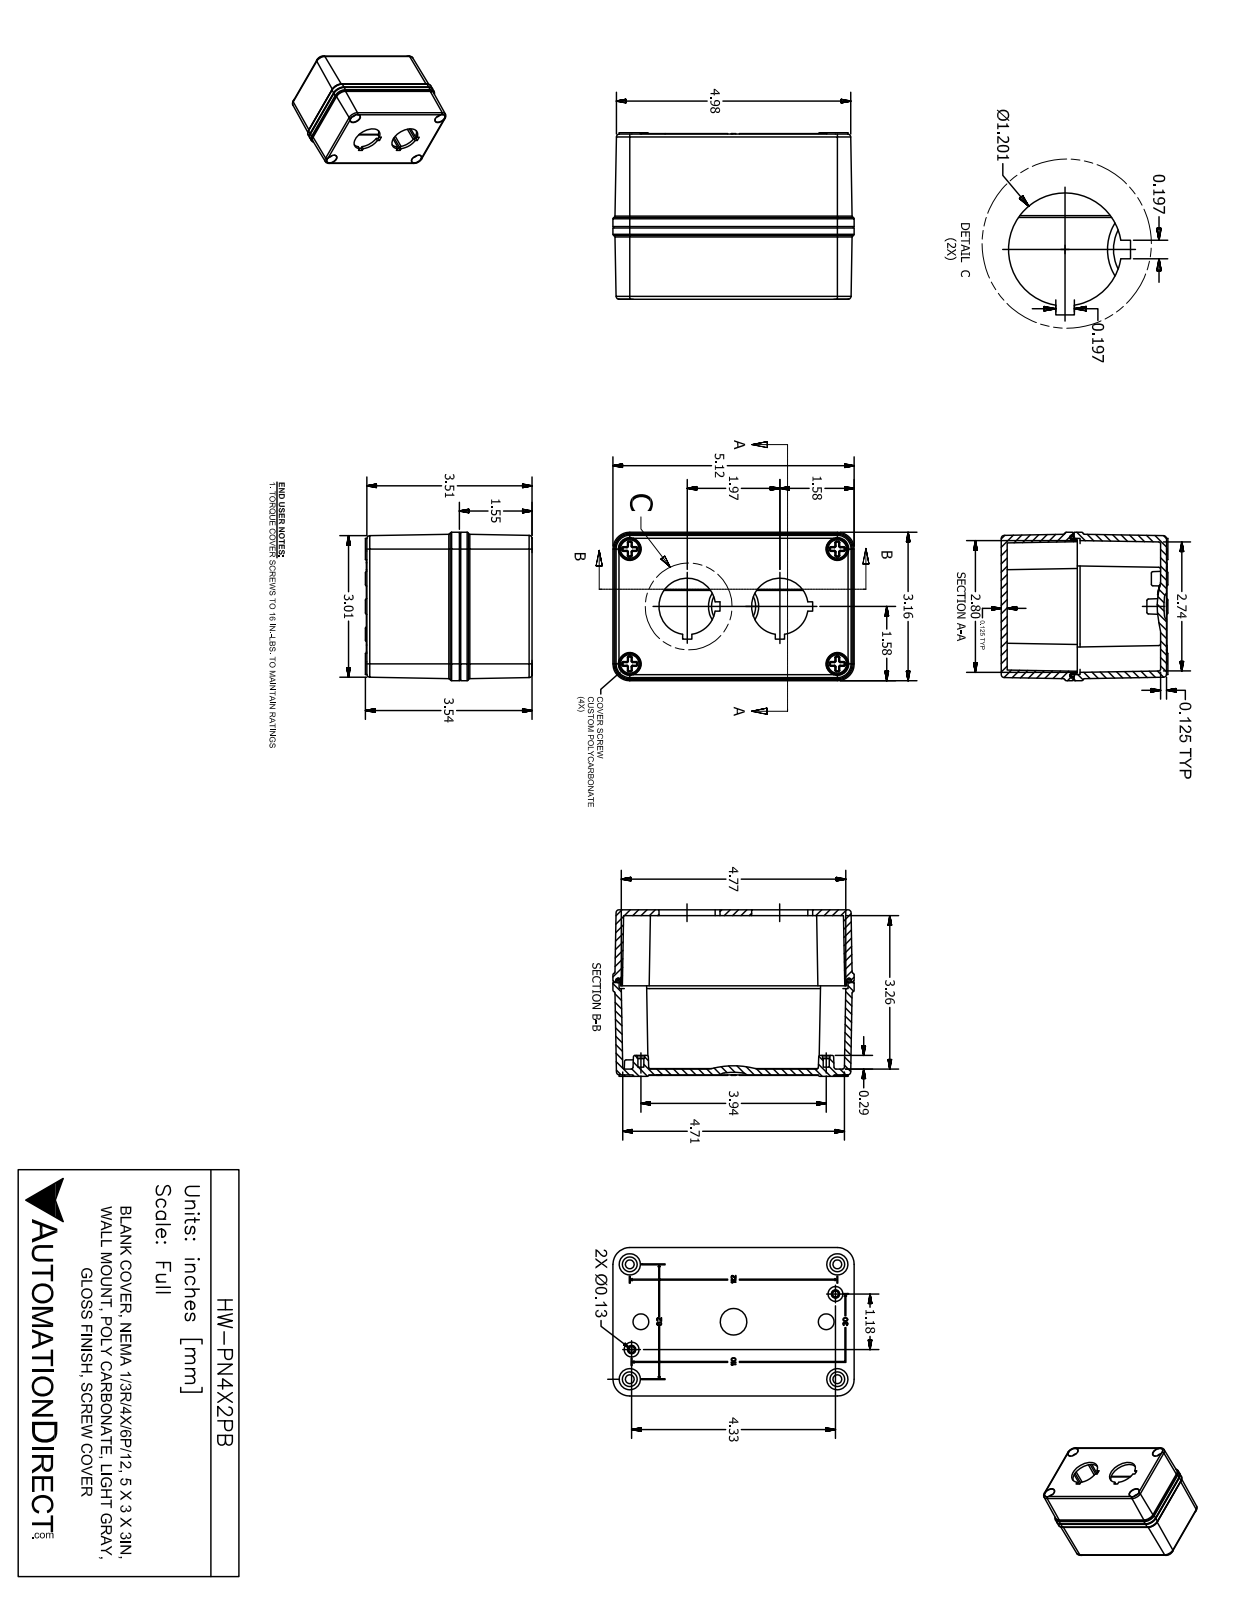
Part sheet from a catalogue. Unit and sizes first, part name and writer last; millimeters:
Units: millimetres
Overall size (bounding box): 130.1 × 89.9 × 80.2
Round holes (diameter × count): ⌀2.5 ×6, ⌀4.7 ×4, ⌀10 ×4, ⌀11.7 ×4, ⌀30.5 ×2
Round bosses / shafts (diameter × count): ⌀12.7 ×4, ⌀11 ×4, ⌀7 ×4, ⌀2.5 ×2
Partial cylindrical surfaces — rounded edges, fillets, slot ends (radius × count): R0.5 ×48, R0.3 ×32, R0.4 ×14, R0.5 ×8, R0.5 ×8, R0.8 ×8, R1 ×8, R1.6 ×8
Main face-to-face distances: 3.4, 4.1, 89.2, 85.7, 86, 82.6, 3.2, 49.9, 46.5, 36.1
Hole centre spacings: 43.8, 86.7, 62, 62, 112, 112, 14.5, 43.8
Volume: 217 300 mm³ · Surface area: 126 600 mm²
Bodies: 7 solids, 1036 faces (224 planar, 368 cylindrical, 444 other)
Part name (STEP PRODUCT): HW-PN4X2PB
STEP written by: SolidWorks 2017 (AUTOMOTIVE_DESIGN)
